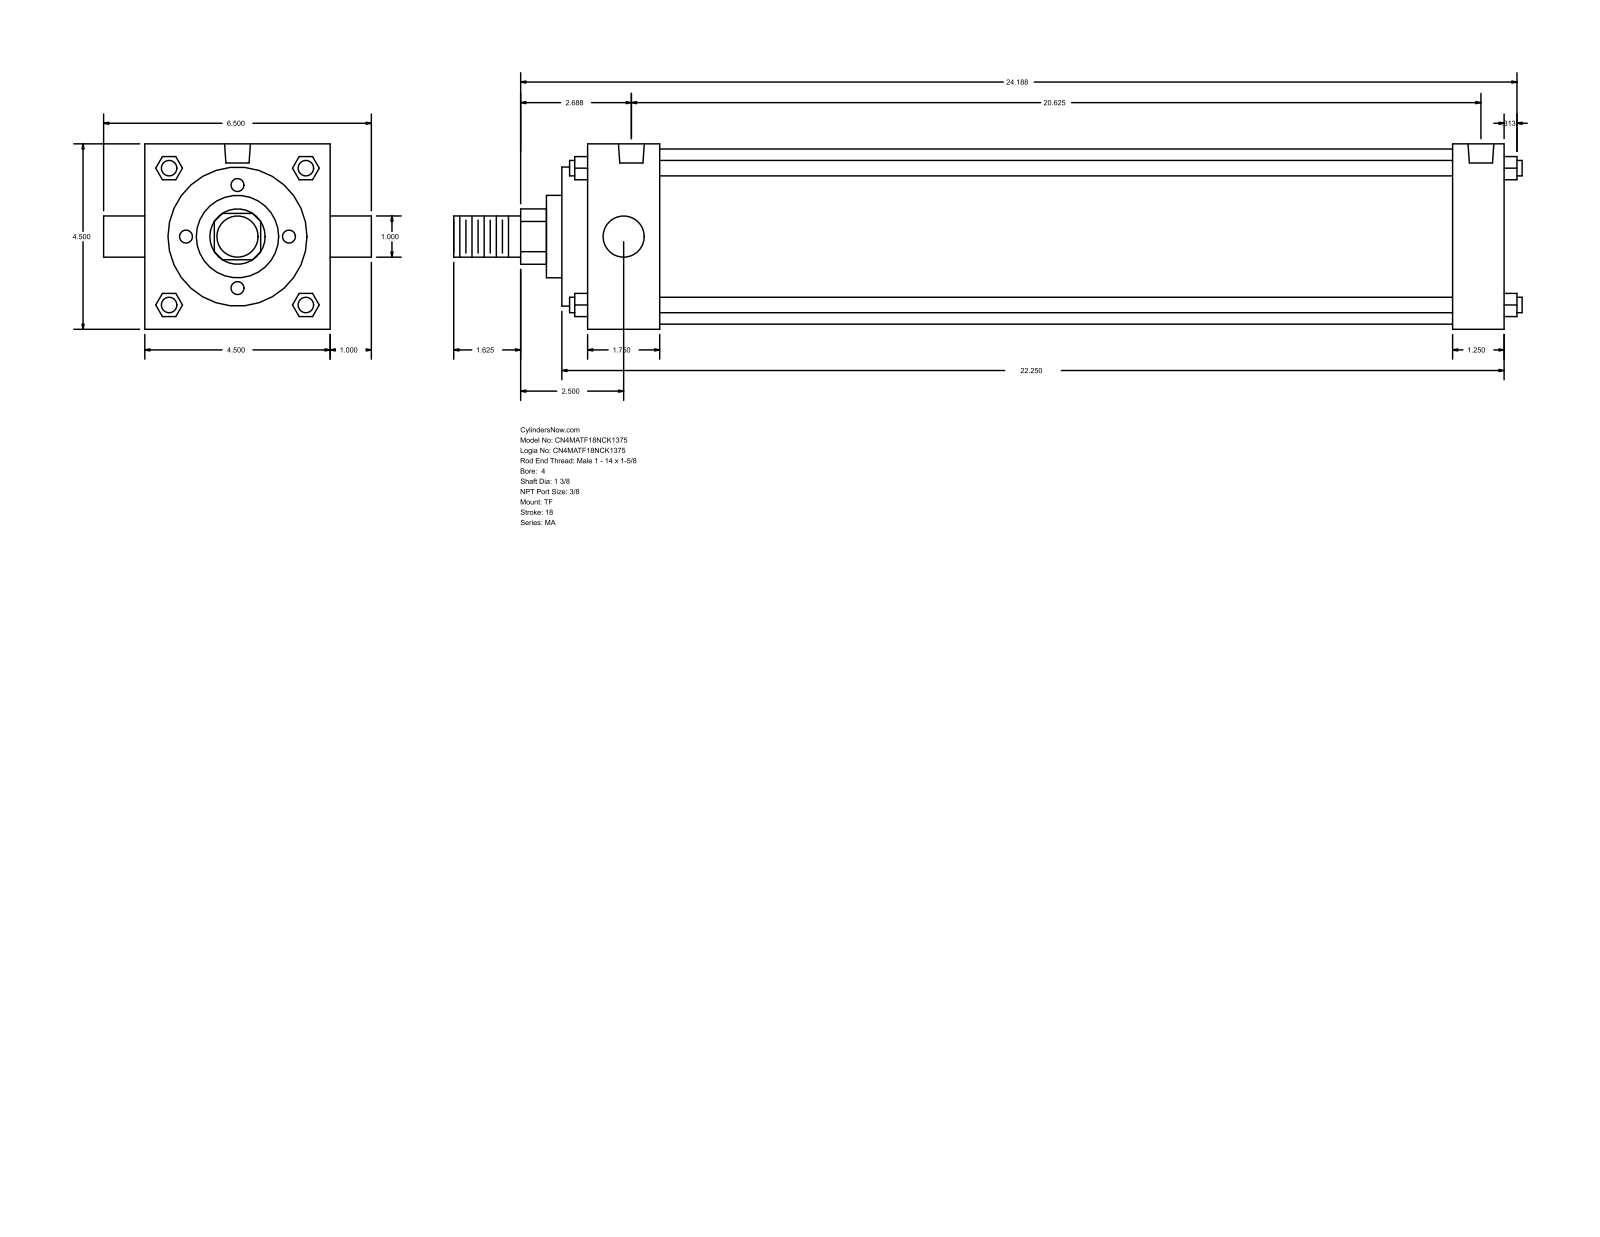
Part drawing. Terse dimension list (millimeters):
name: MA_TF__0400_1.375
written by: GSSL Pune (CONFIG_CONTROL_DESIGN)
unit: mm
bodies: 0 solids, 122 faces (93 planar, 29 cylindrical, 0 other)
size: 658.81 × 165.1 × 114.3
holes: 3× ⌀11.11, 2× ⌀15.93
bosses: 4× ⌀9.53, 2× ⌀25.4, 1× ⌀107.95, 1× ⌀85.72, 1× ⌀50.8, 1× ⌀34.92
rounds: 1× R17.06
face distances: 114.3, 565.15, 581.02, 15.87, 549.27, 533.4, 31.75, 60.32, 44.45, 488.95
hole spacings: 4.76, 4.77, 514.35, 519.11, 519.12, 523.88
